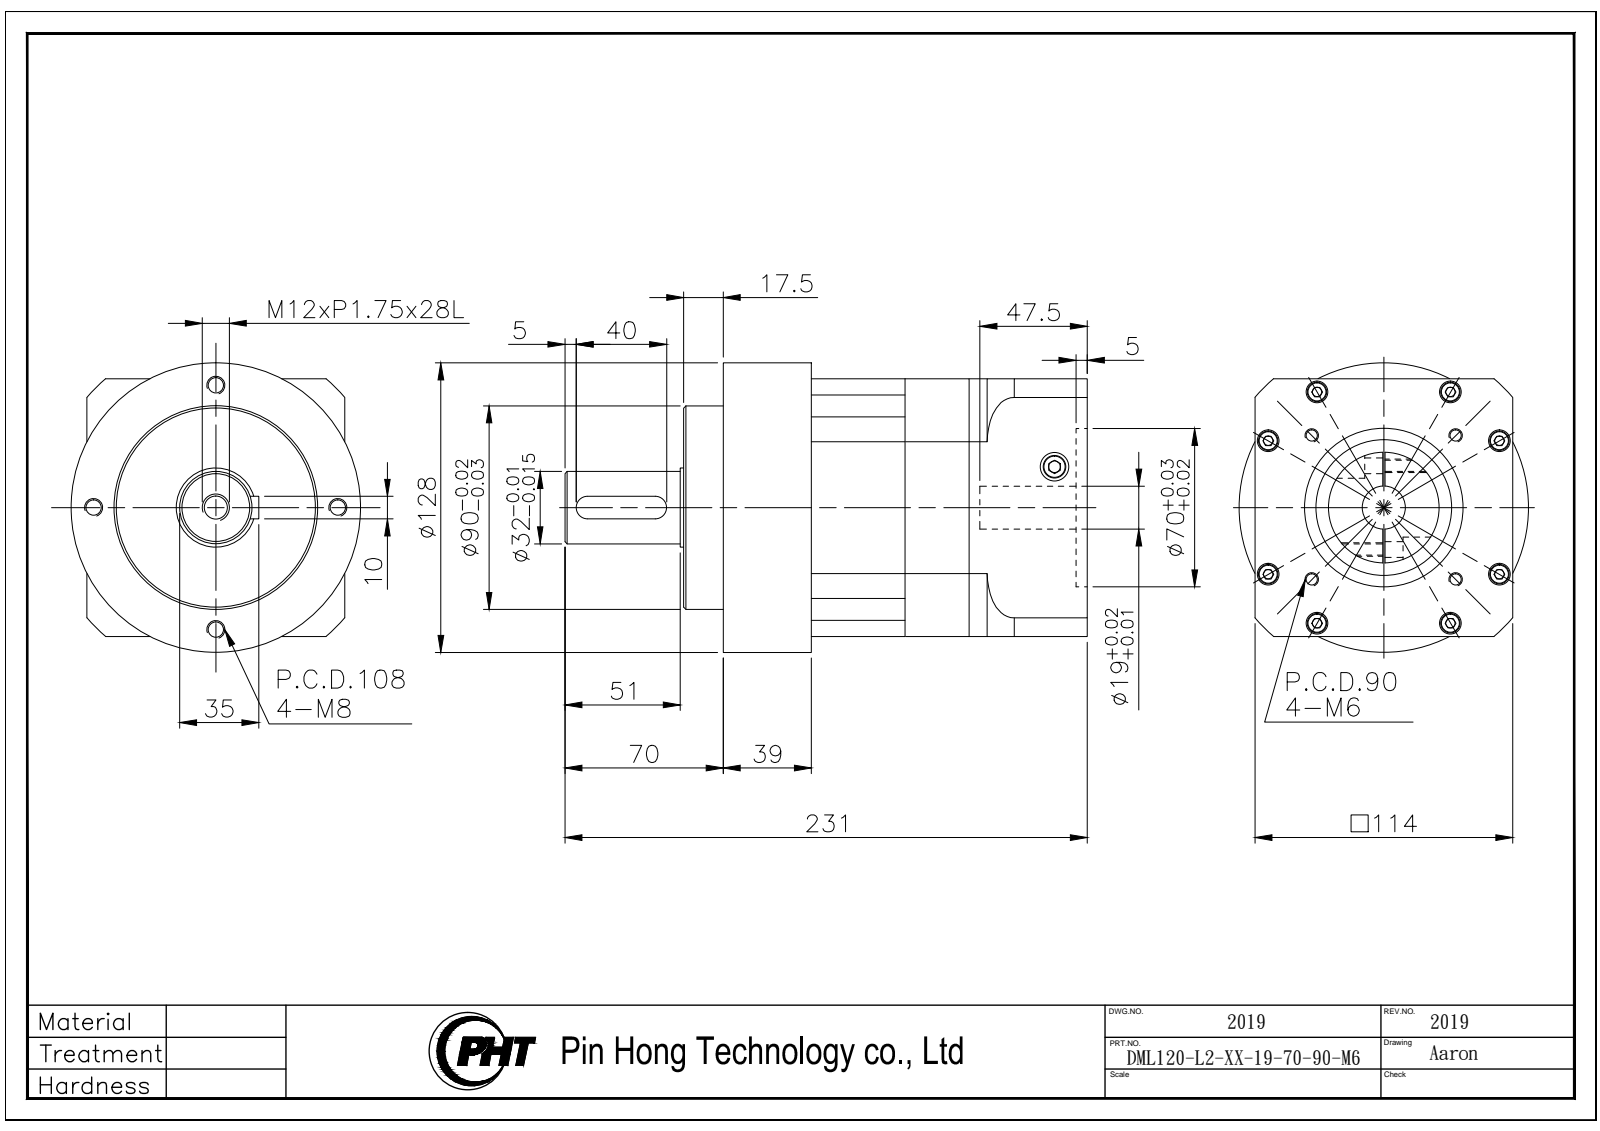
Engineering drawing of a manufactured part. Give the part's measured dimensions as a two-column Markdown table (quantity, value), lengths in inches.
| quantity | value |
| --- | --- |
| part name | DML120-L2-XX-19-70-90-M6_2019 |
| STEP written by | SolidWorks 2016 (AUTOMOTIVE_DESIGN) |
| units | inches |
| bodies | 4 solids, 271 faces (114 planar, 117 cylindrical, 40 other) |
| overall size | 9.094 × 5.039 × 5.039 |
| volume | 123.1 in³ |
| surface area | 329.7 in² |
| round holes (diameter × count) | 0.209 × 8, 0.374 × 8, 0.197 × 4, 0.268 × 4, 0.5 × 2, 0.402 × 1, 0.748 × 1, 2.362 × 1, 2.756 × 1 |
| round bosses / shafts (diameter × count) | 0.335 × 8, 5.039 × 1, 3.543 × 1, 1.929 × 1, 1.378 × 1, 1.26 × 1 |
| partial cylindrical surfaces (radius × count) | 0.276 × 4, 0.197 × 2, 2.953 × 1 |
| main face-to-face distances | 2.744, 1.114, 1.63, 4.488, 3.173, 2.059, 4.803, 2.224, 6.339, 4.28 |
| hole center spacings | 2.323, 0.765, 1.167, 1.527, 2.231, 2.531, 3.266, 3.285 |
